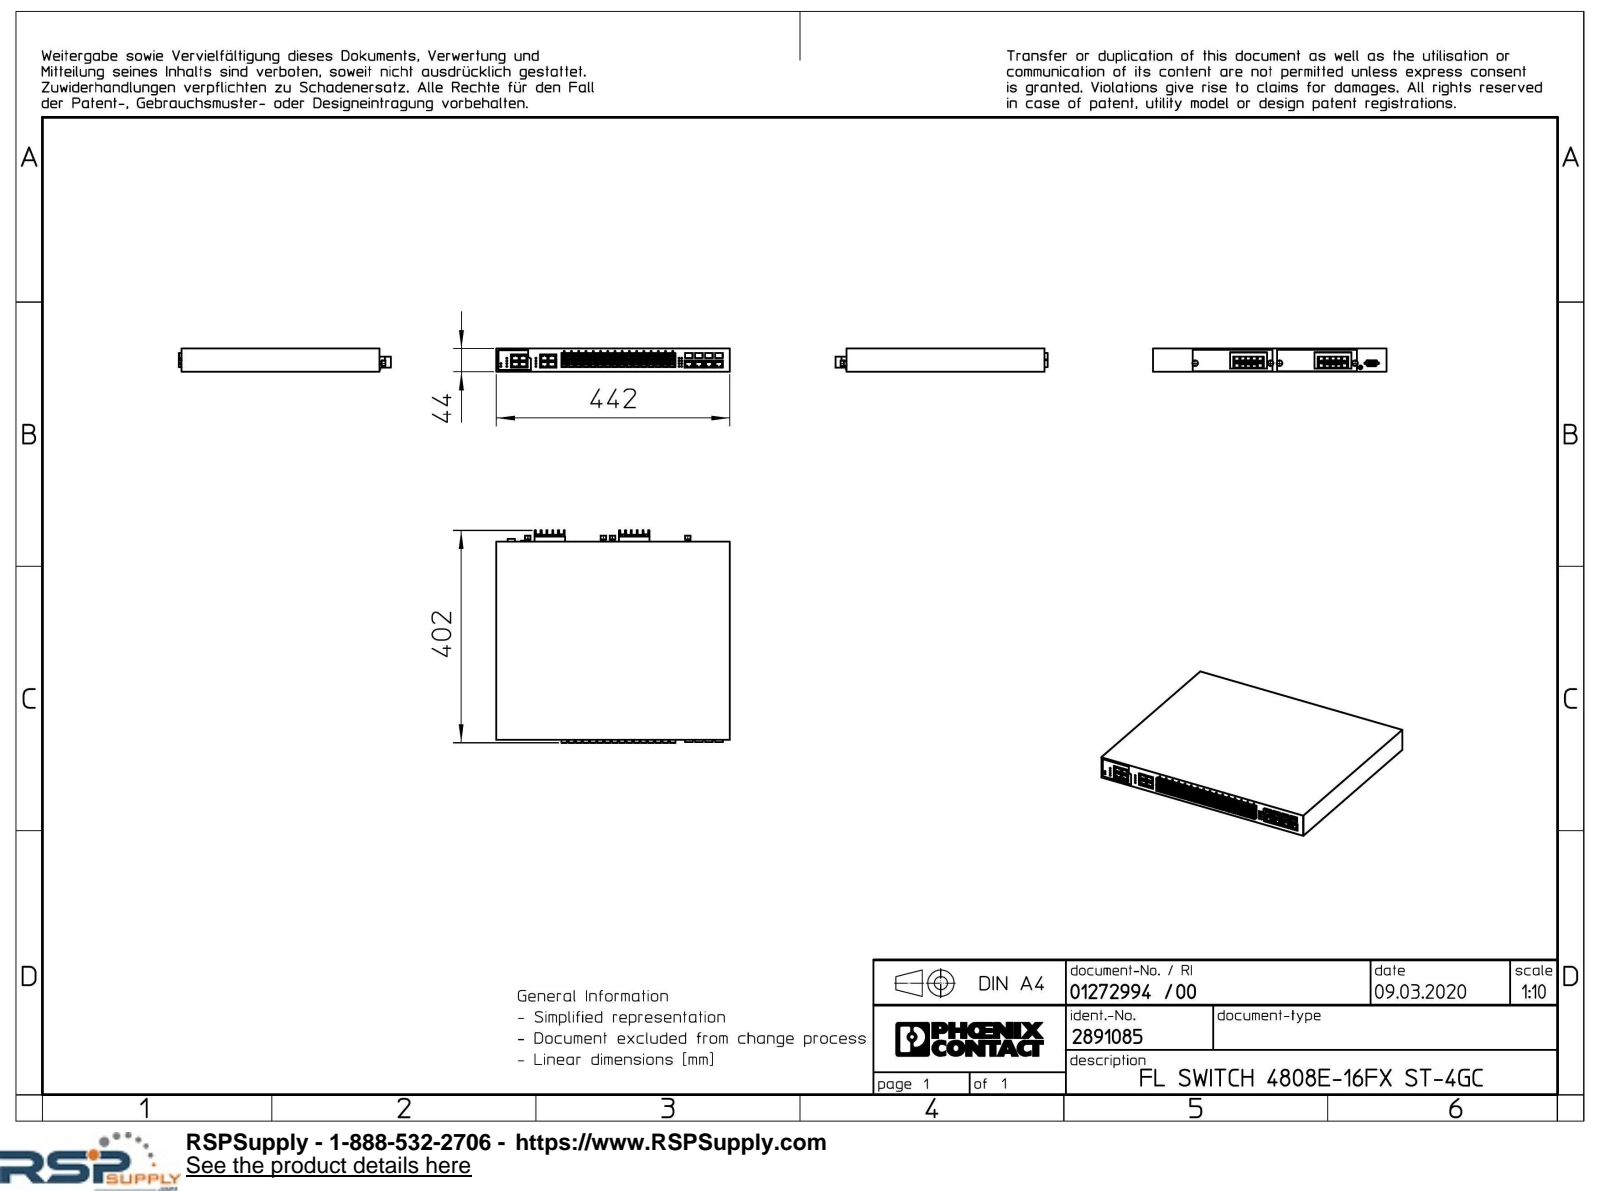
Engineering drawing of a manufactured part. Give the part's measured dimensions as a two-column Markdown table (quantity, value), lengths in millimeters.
| quantity | value |
| --- | --- |
| part name | FL_SWITCH_4808E_16FX_..._4GC-select |
| STEP written by | Creo Elements/Direct Modeling 20.1A 29-Sep-2018 (C) Parametric Technology GmbH (AUTOMOTIVE_DESIGN) |
| units | millimeters |
| bodies | 1 solid, 1324 faces (1060 planar, 264 cylindrical, 0 other) |
| overall size | 442 × 401.83 × 44 |
| volume | 7 330 000 mm³ |
| surface area | 436 181 mm² |
| round holes (diameter × count) | 2 × 34, 3 × 32, 1 × 9, 3.2 × 2 |
| round bosses / shafts (diameter × count) | 4 × 32, 6 × 14, 10.5 × 4, 7 × 1 |
| partial cylindrical surfaces (radius × count) | 1 × 4, 2.5 × 4 |
| main face-to-face distances | 44, 442, 374.9, 375, 11, 374.8, 13.97, 0.85, 11.85, 5.53 |
| hole center spacings | 5.08, 3.16, 10.16, 2.77, 7.13, 55.03, 271.25, 276.25 |
